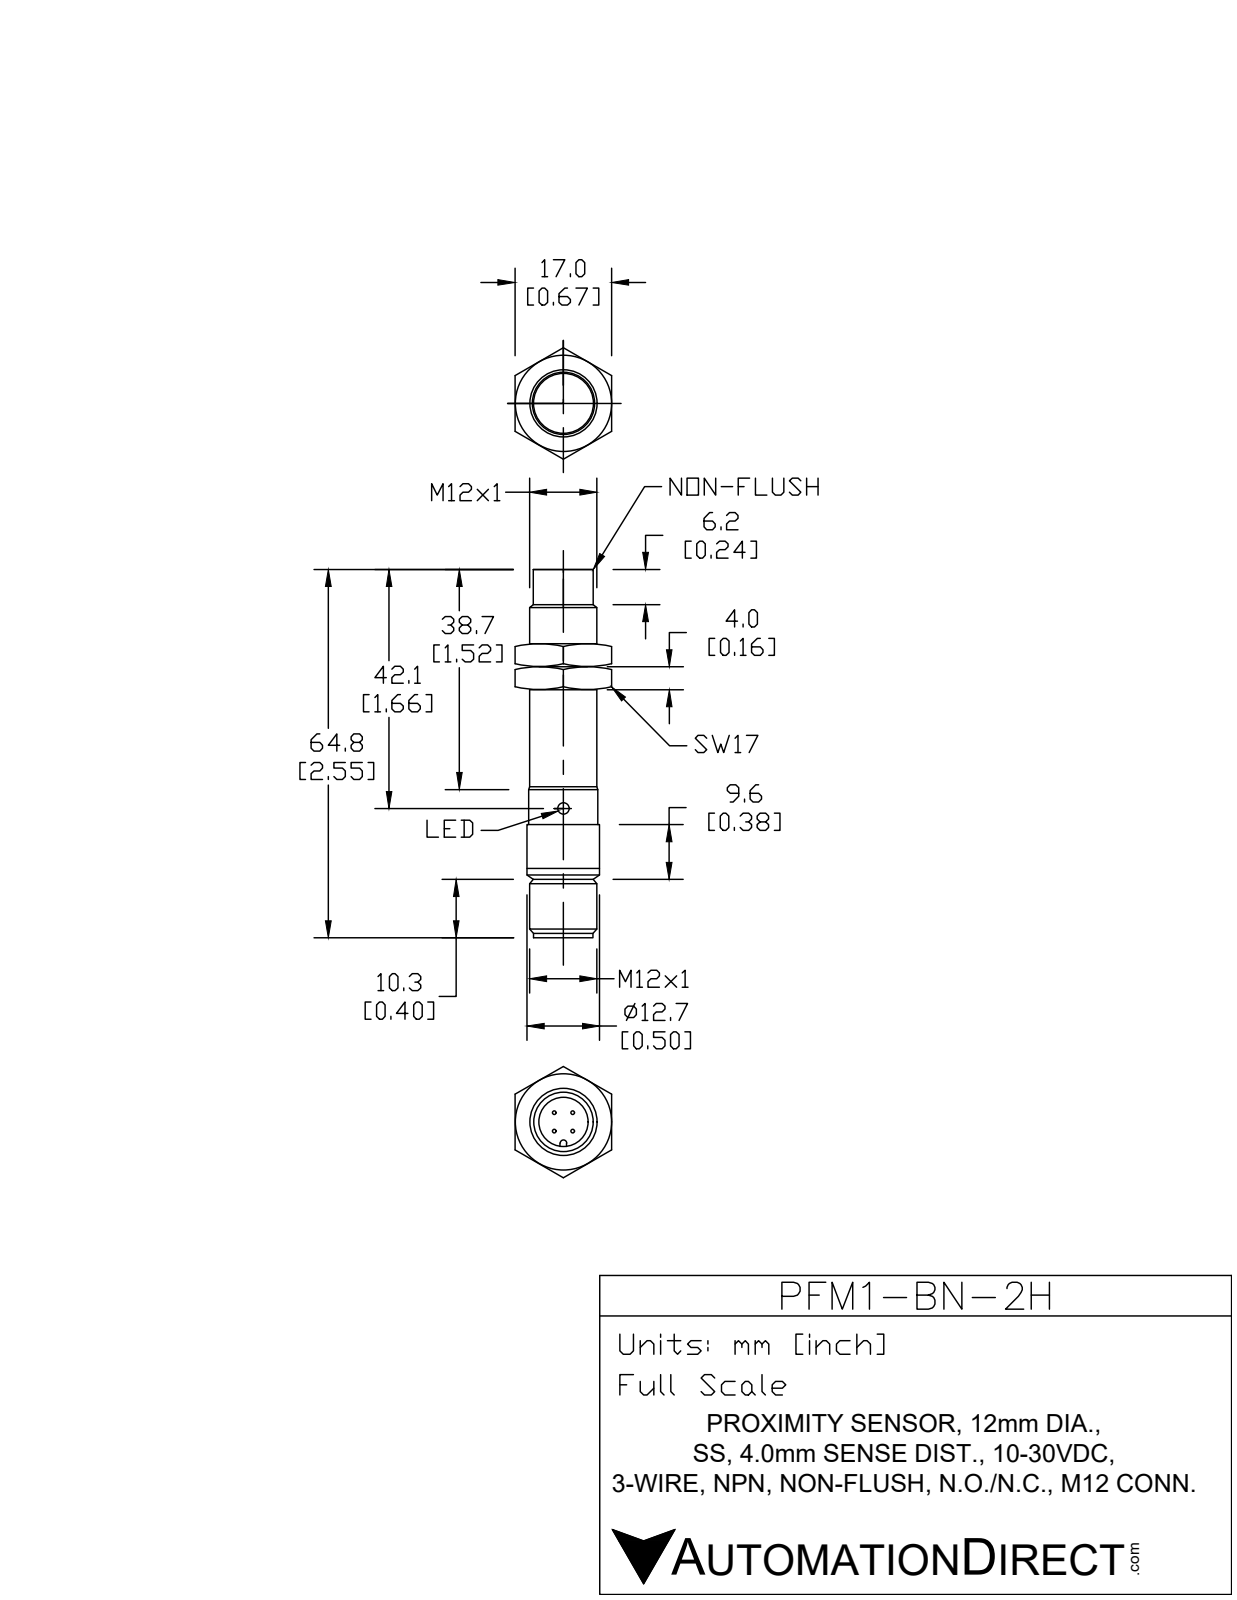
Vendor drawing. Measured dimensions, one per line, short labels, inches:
name: PFM1-BN-2H
written by: SolidWorks 2017 (AUTOMOTIVE_DESIGN)
unit: in
bodies: 4 solids, 73 faces (11 planar, 36 cylindrical, 26 other)
size: 2.543 × 0.5 × 0.5
volume: 0.409 in³; area: 6.284 in²
holes: 1× ⌀0.118, 1× ⌀0.331, 1× ⌀0.335, 1× ⌀0.374
bosses: 4× ⌀0.039, 1× ⌀0.5, 1× ⌀0.472, 1× ⌀0.413, 1× ⌀0.394, 1× ⌀0.37
rounds: 1× R0.024, 1× R0.219
face distances: 1.839, 1.909, 0.071, 0.236, 2.075, 2.146, 2.193, 1.957, 0.118, 0.047
